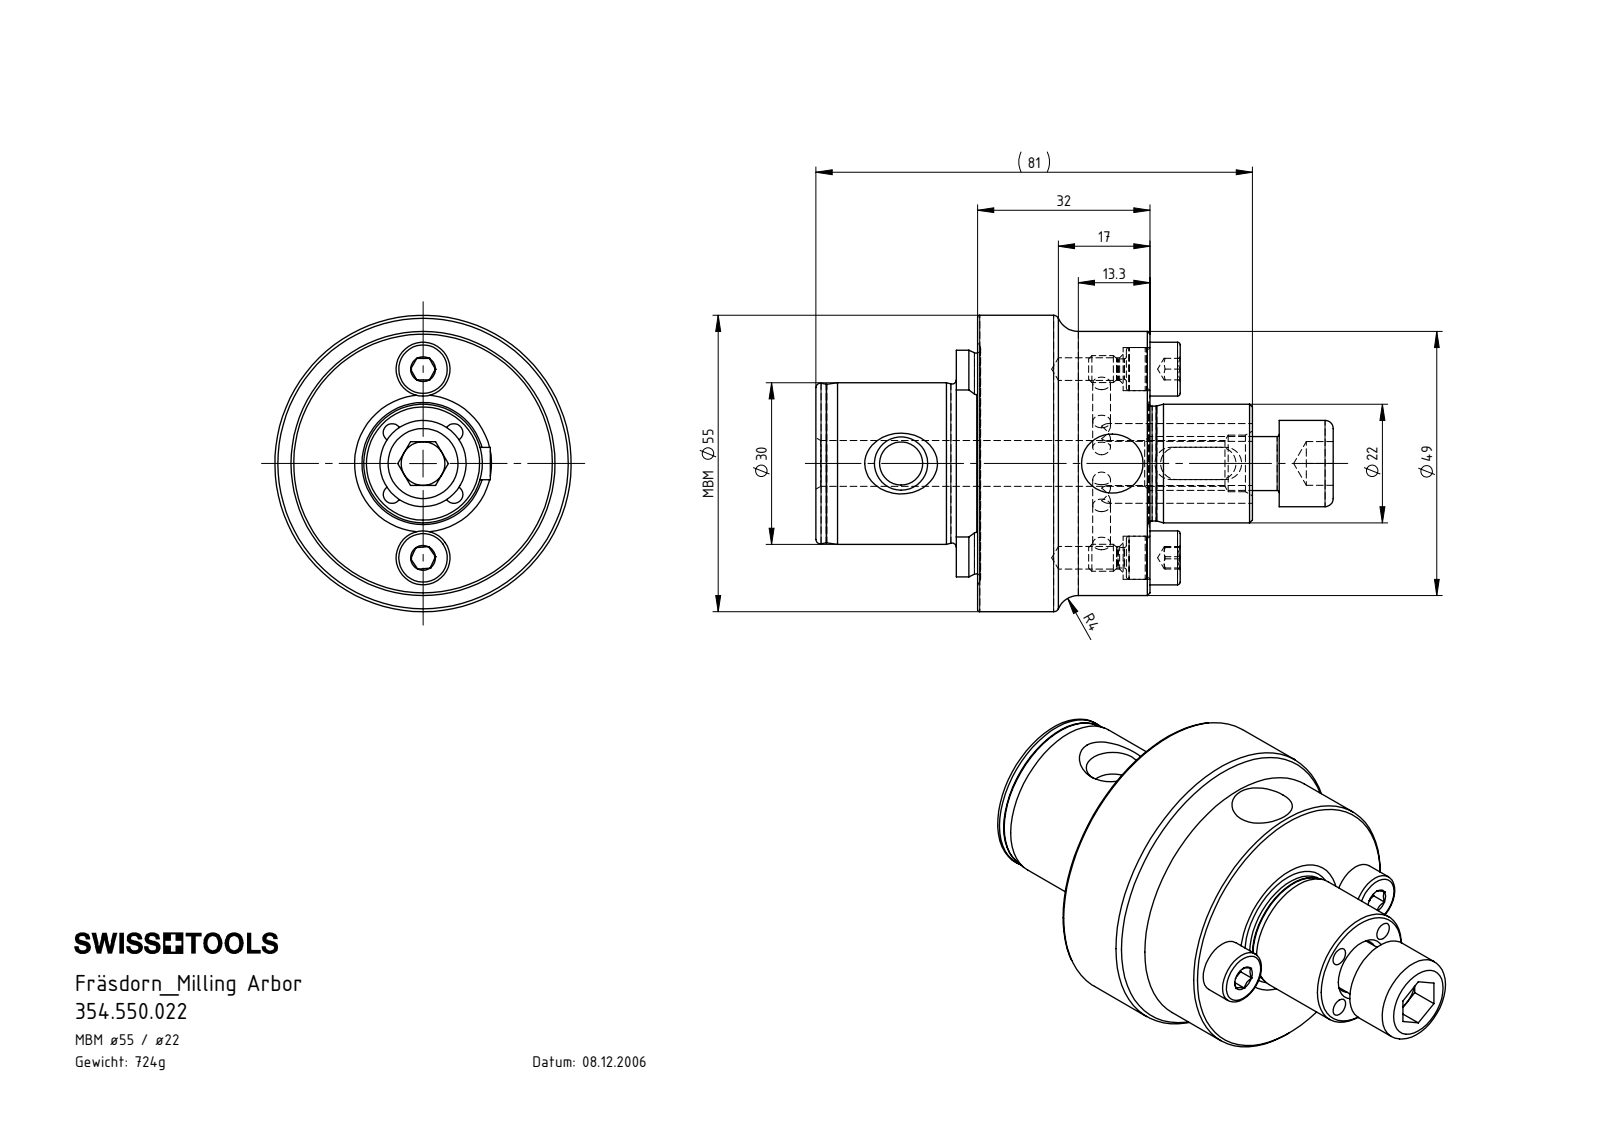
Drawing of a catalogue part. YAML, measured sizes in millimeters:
part_name: "MB5-D22.K01.032_C; D22-ER1.K62.008_A; D22-ER1.K63.016_A; MB5.D22.K01.032 (+4 more)"
step_written_by: "SolidWorks 2017 (AUTOMOTIVE_DESIGN)"
units: millimeters
bodies: {solids: 8, faces: 235, planar: 77, cylindrical: 89, other: 69}
overall_size: [96, 55, 55]
volume: 98527
surface_area: 24082
round_holes:
  - {diameter: 2.5, count: 9}
  - {diameter: 3.3, count: 4}
  - {diameter: 8, count: 2}
  - {diameter: 4.5, count: 1}
  - {diameter: 8.5, count: 1}
  - {diameter: 10.5, count: 1}
  - {diameter: 15, count: 1}
round_bosses_or_shafts:
  - {diameter: 55, count: 1}
  - {diameter: 49, count: 1}
  - {diameter: 30, count: 1}
  - {diameter: 28, count: 1}
  - {diameter: 22, count: 1}
  - {diameter: 21.3, count: 1}
  - {diameter: 16, count: 1}
  - {diameter: 10, count: 1}
partial_cylinders:
  - {radius: 3, count: 4}
  - {radius: 5, count: 1}
  - {radius: 21.02, count: 1}
face_to_face_distances: [32, 30, 62, 7, 96, 66, 34, 8, 26.05, 3.95]
hole_center_spacings: [10, 17.32, 20, 3.01, 7.15, 8.13, 11.14, 14.43]
